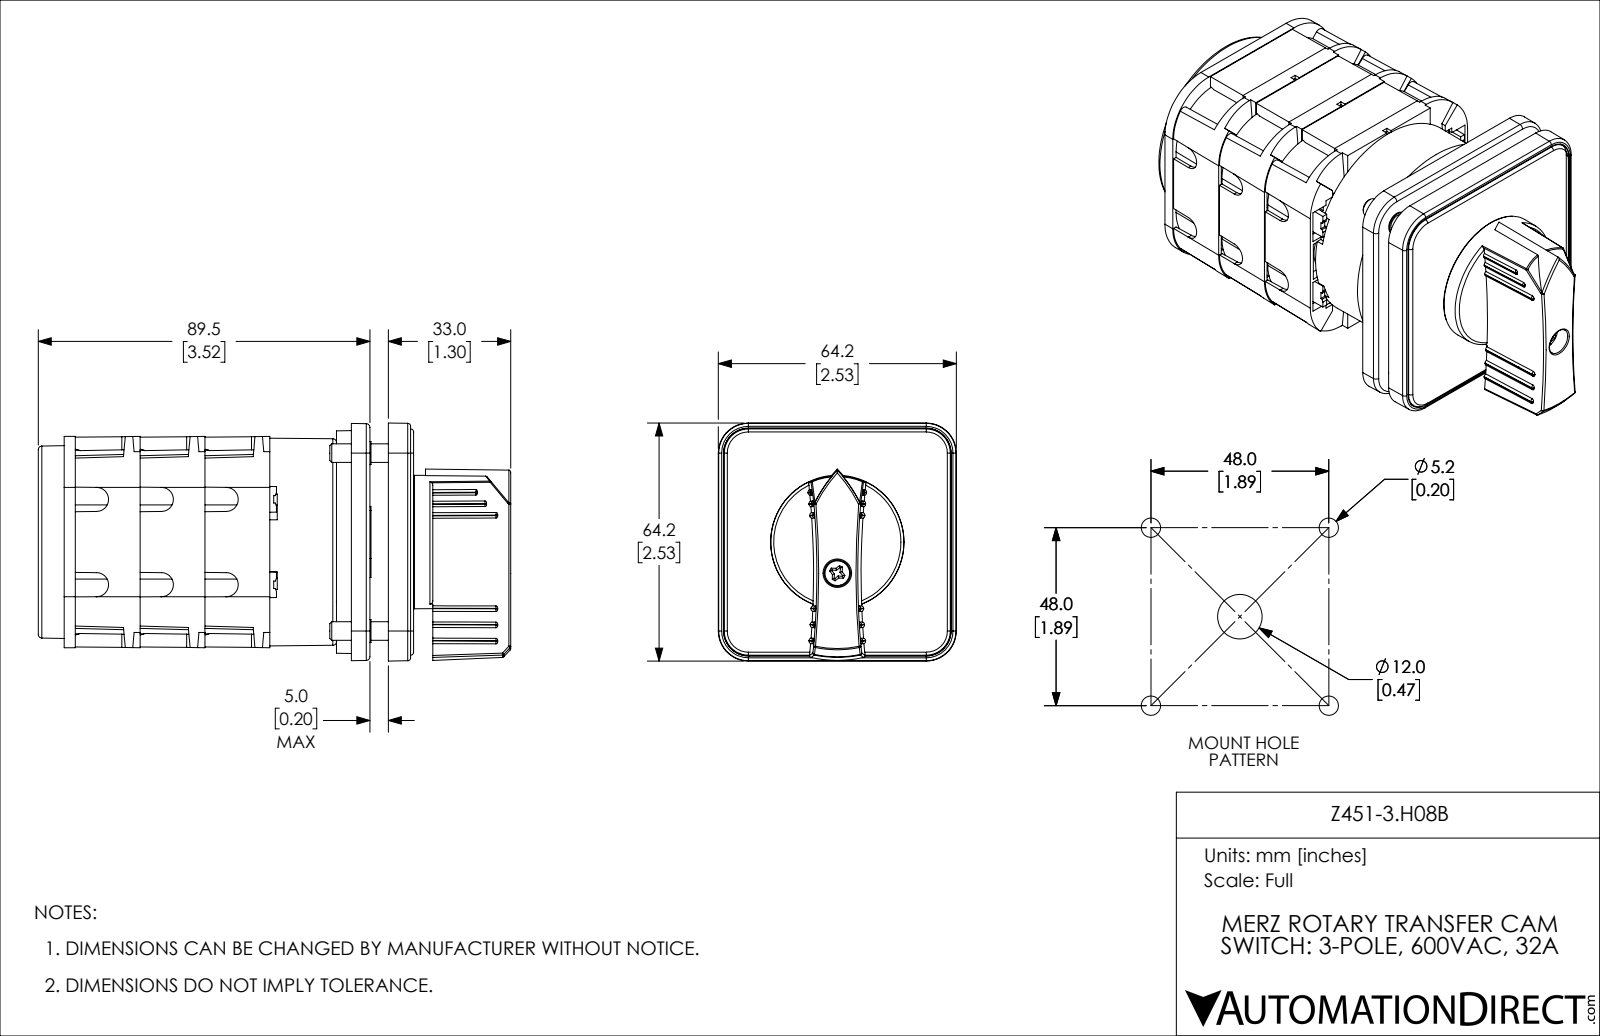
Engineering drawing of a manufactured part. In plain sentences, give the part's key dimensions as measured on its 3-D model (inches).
The part is named "Z451-3.H08B". Its 3-D file was written by "SolidWorks 2021 (CONFIG_CONTROL_DESIGN)". It is 23 solids with 3861 faces: 2210 planar, 375 cylindrical and 1276 other. Overall it measures 5.02 by 2.528 by 2.528 inches. Its volume is 15.7 cubic inches and its surface area 175.9 square inches. Round holes: 6 of diameter 0.315, 4 of diameter 0.012, 4 of diameter 0.157, 4 of diameter 0.197, 4 of diameter 0.205, 4 of diameter 0.374, 2 of diameter 0.24, 1 of diameter 0.394, 1 of diameter 0.512, 1 of diameter 0.551, 1 of diameter 0.925. Round bosses or shafts: 5 of diameter 0.197, 4 of diameter 0.366, 4 of diameter 0.319, 4 of diameter 0.287, 2 of diameter 0.315, 2 of diameter 0.157, 2 of diameter 0.139, 1 of diameter 0.622. Partial cylindrical surfaces (rounded edges, fillets, slot ends): 17 of radius 0.039, 14 of radius 0.008, 11 of radius 0.031, 8 of radius 0.169, 6 of radius 0.02, 6 of radius 0.098, 6 of radius 0.128, 4 of radius 0.006. The main face-to-face distances are 0.098, 0.689, 0.748, 0.394, 0.591, 2.146, 1.378, 0.071, 0.465, 0.197. The hole center spacings are 0.802, 1.67, 0.334, 0.355, 0.368, 0.374, 0.644, 0.648.
